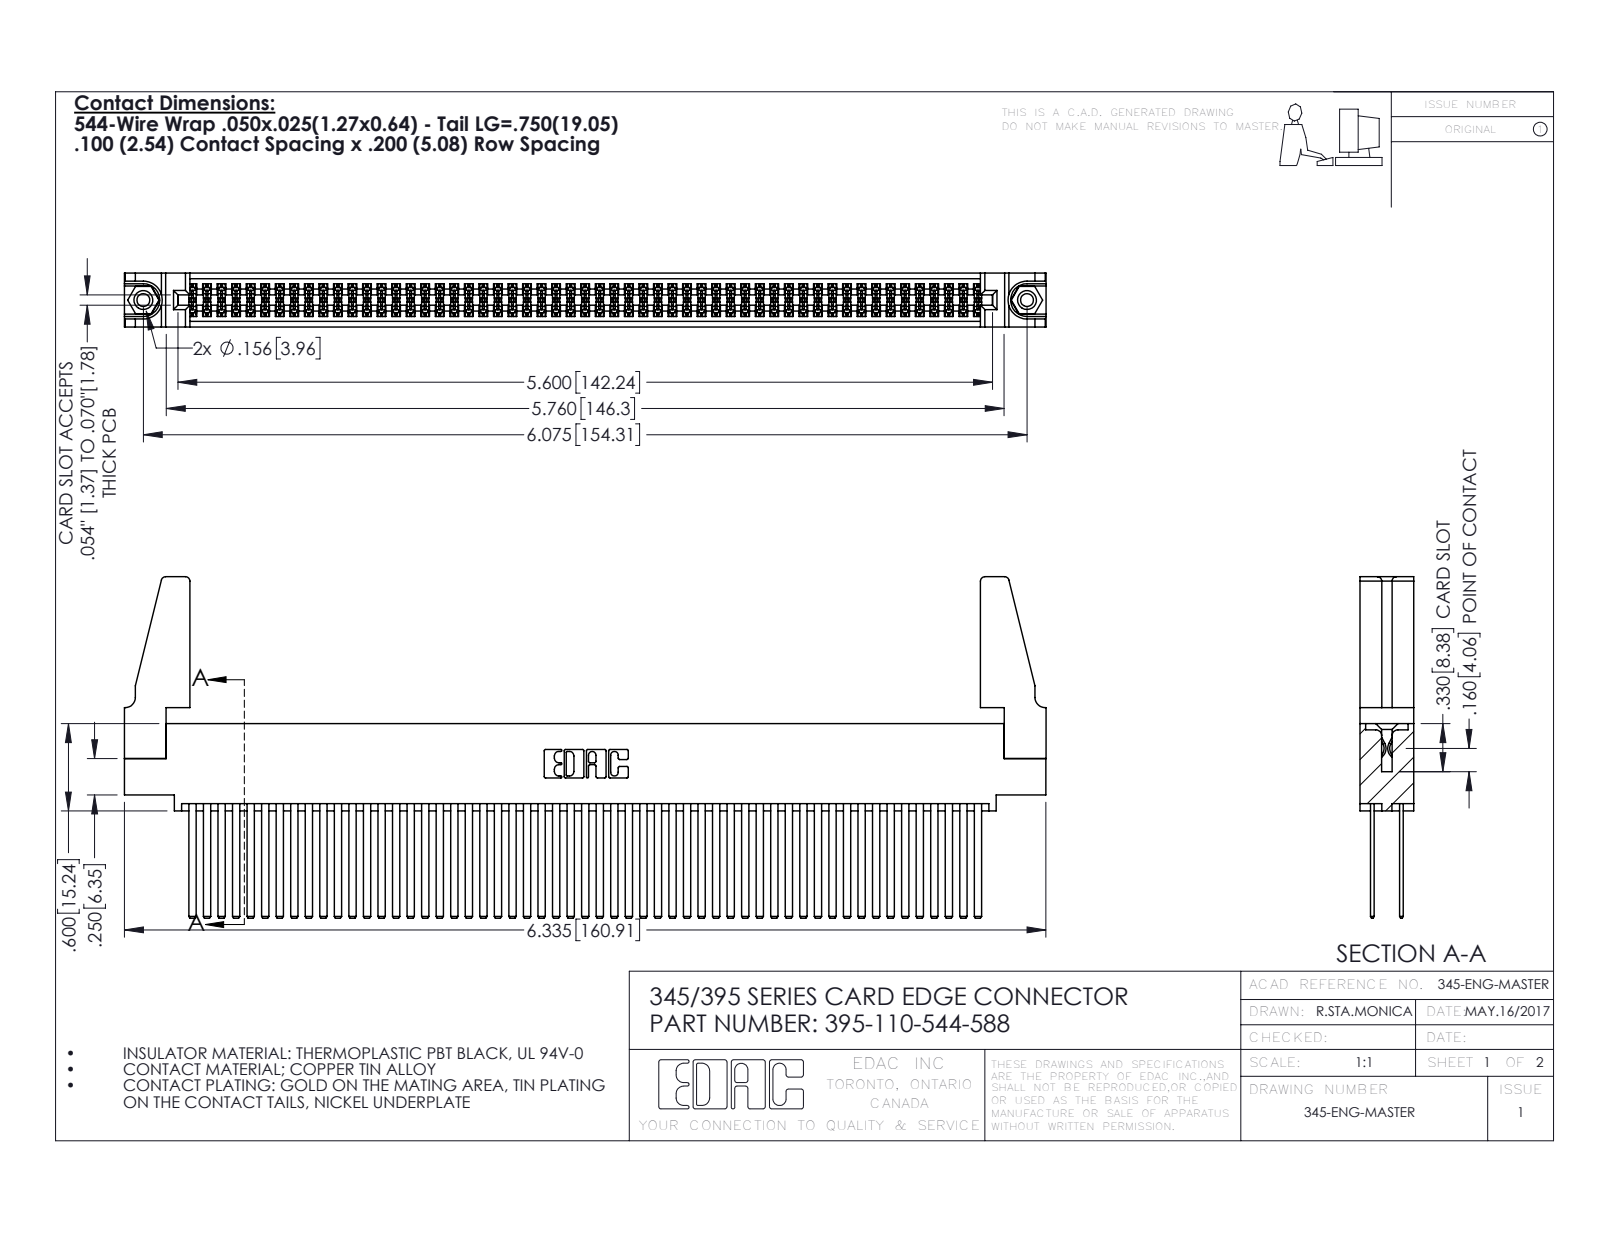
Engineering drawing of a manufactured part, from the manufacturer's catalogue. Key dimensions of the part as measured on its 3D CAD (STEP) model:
Part name (STEP PRODUCT): 345-292-001_345-293-144; 345-250-001_345-250-001-102; 395-110-544-588; 345 Part_0.110 Offset - 0.156 Dia-TH (+1 more)
STEP written by: SolidWorks 2016 (CONFIG_CONTROL_DESIGN)
Units: inches
Bodies: 115 solids, 5094 faces (3346 planar, 1732 cylindrical, 16 other)
Overall size (bounding box): 6.336 × 2.347 × 0.37
Volume: 1.249 in³ · Surface area: 51.84 in²
Round holes (diameter × count): ⌀0.089 ×2, ⌀0.125 ×2, ⌀0.156 ×2, ⌀0.064 ×1
Round bosses / shafts (diameter × count): ⌀0.155 ×2
Partial cylindrical surfaces — rounded edges, fillets, slot ends (radius × count): R0.006 ×165, R0.01 ×22, R0.03 ×8, R0.007 ×6, R0.031 ×6, R0.026 ×3, R0.014 ×2, R0.019 ×2
Main face-to-face distances: 0.072, 0.298, 0.2, 0.098, 0.272, 0.025, 0.225, 0.37, 0.175, 0.149
Hole centre spacings: 0.27, 5.839, 6.075
